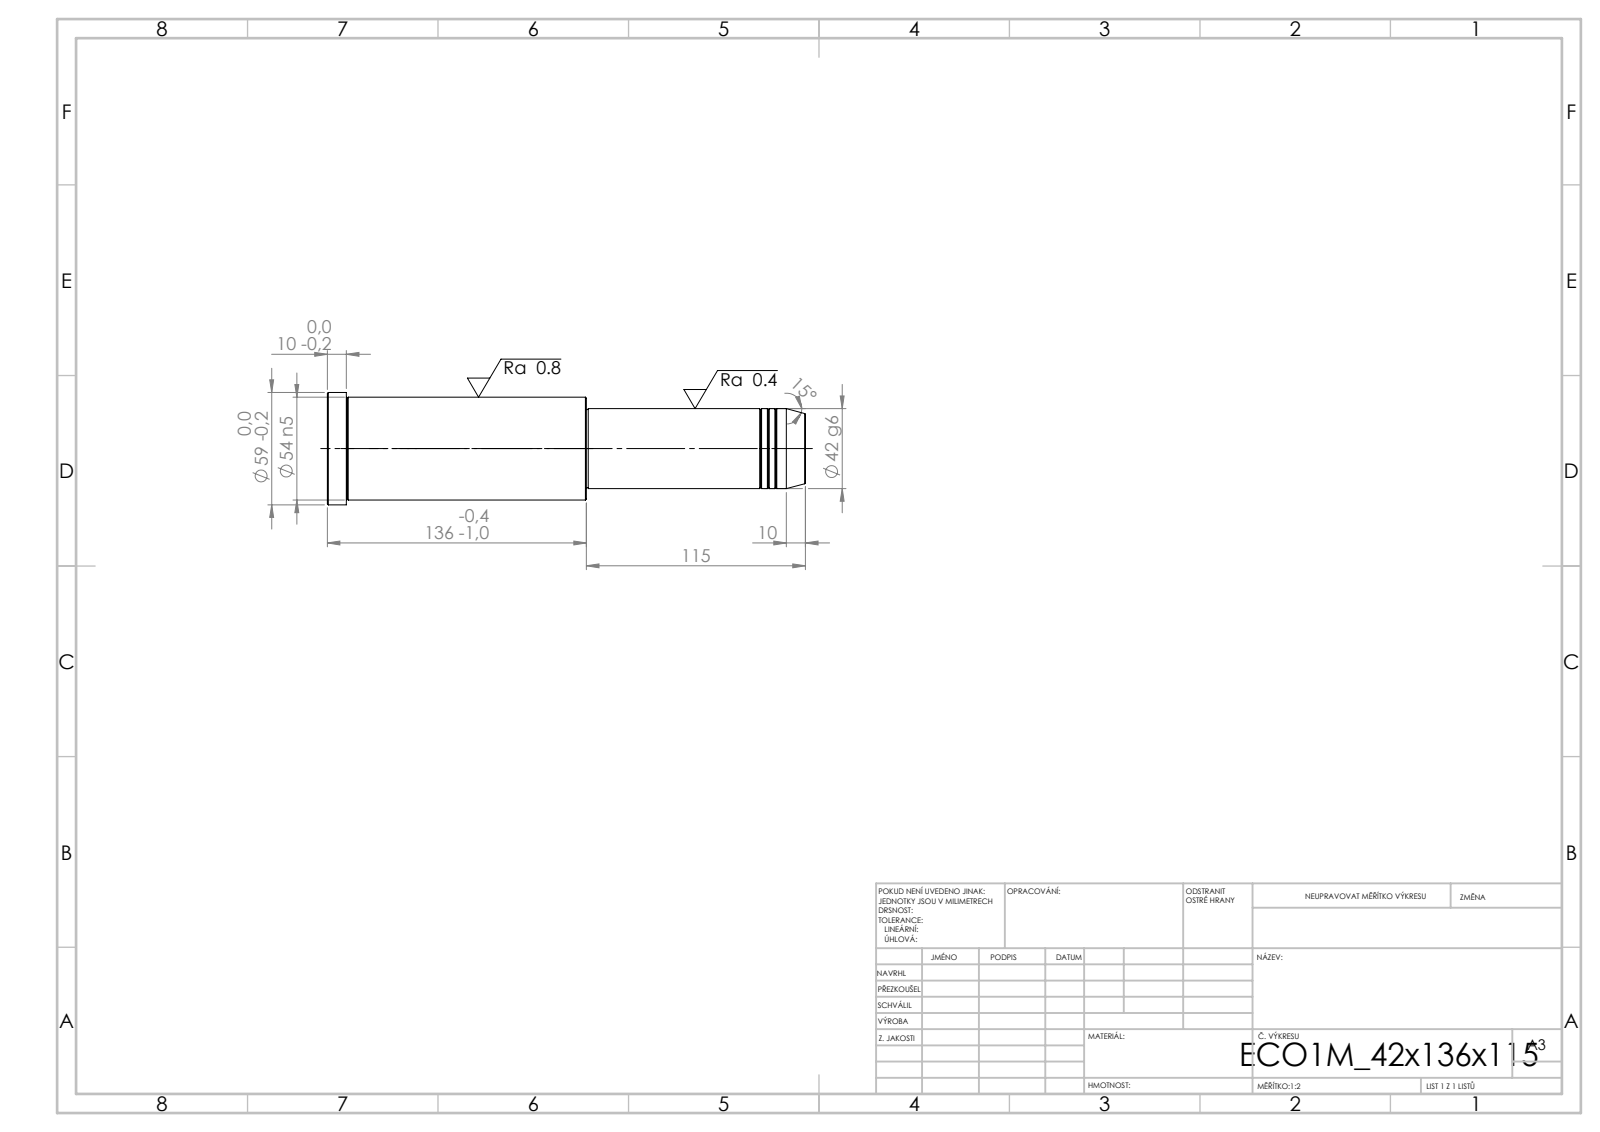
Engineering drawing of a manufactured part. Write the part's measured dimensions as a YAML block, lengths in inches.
step_written_by: "SolidWorks 2019 (CONFIG_CONTROL_DESIGN)"
units: inches
bodies: {solids: 1, faces: 43, planar: 5, cylindrical: 14, other: 24}
overall_size: [9.882, 2.323, 2.323]
volume: 28.88
surface_area: 67.92
round_bosses_or_shafts:
  - {diameter: 2.323, count: 1}
  - {diameter: 2.126, count: 1}
  - {diameter: 1.654, count: 1}
  - {diameter: 1.614, count: 1}
face_to_face_distances: [9.882, 4.528, 5.354, 9.488, 4.961, 0.394, 4.488, 0.039, 5, 5.394]
